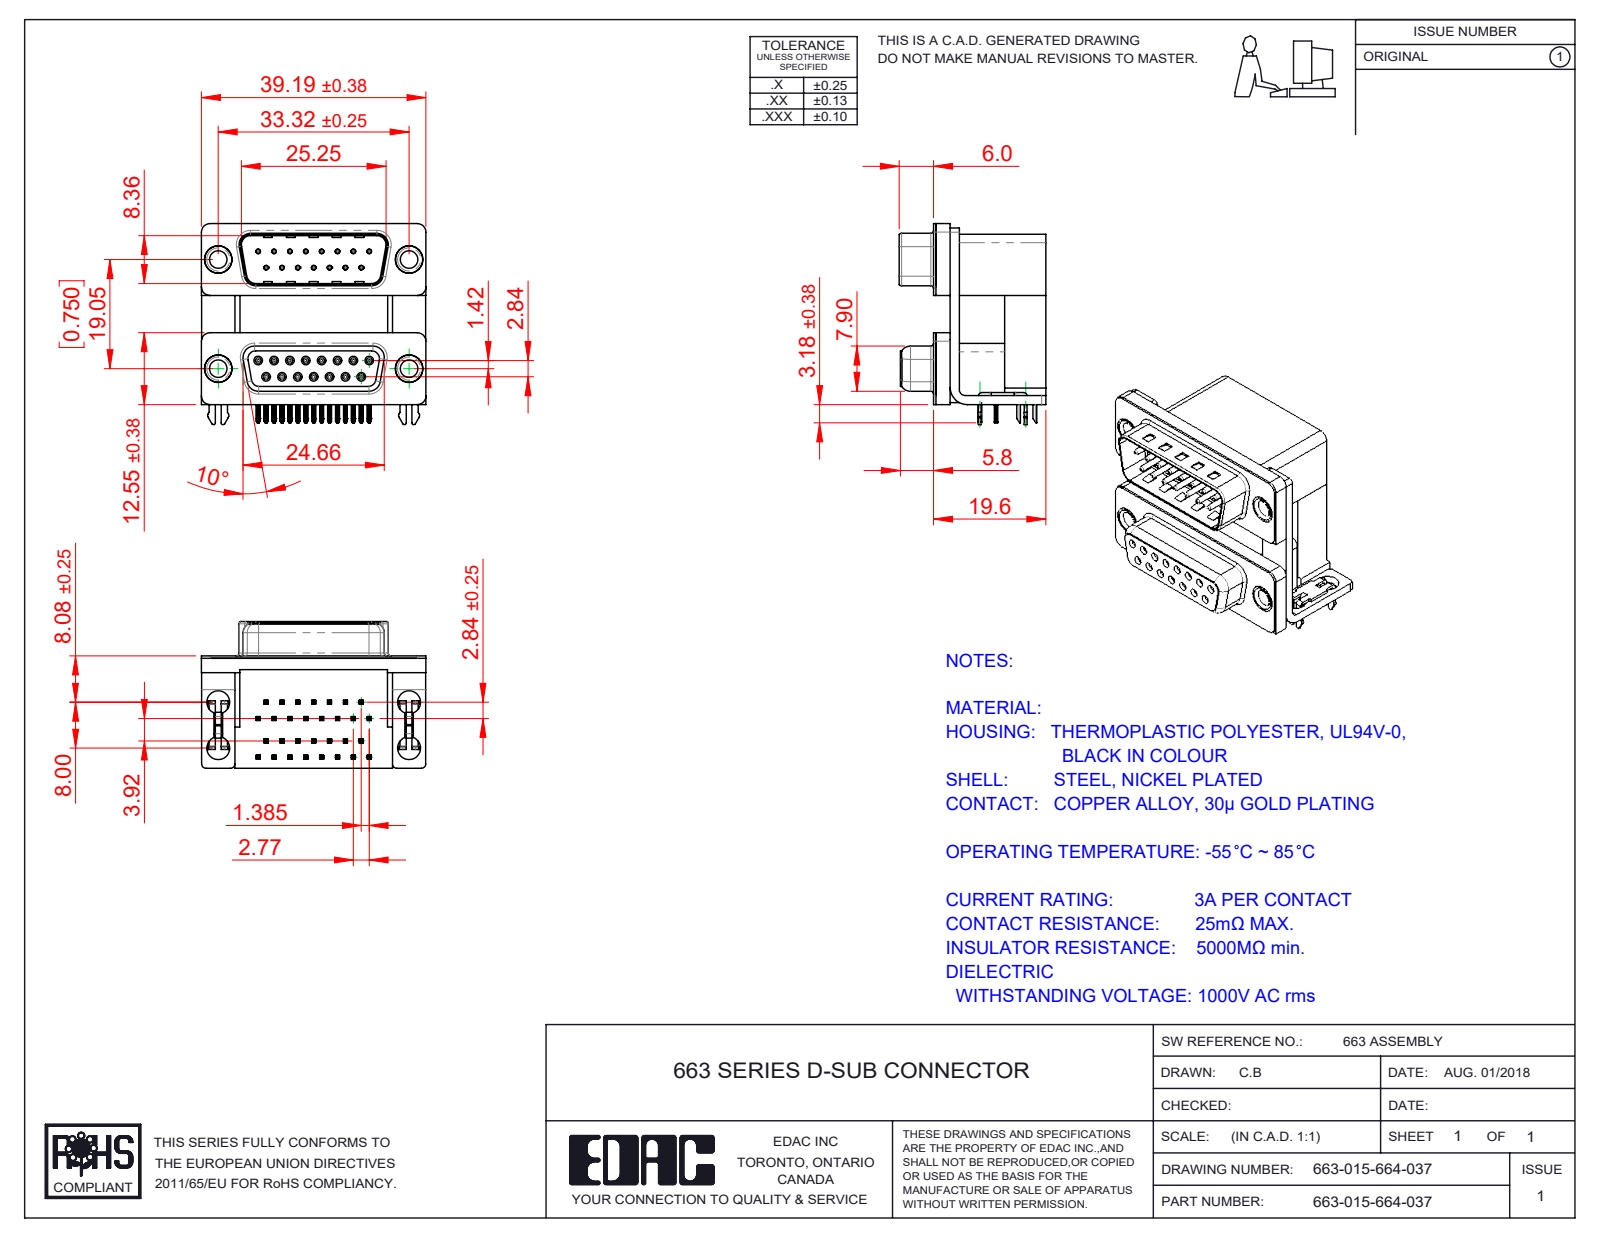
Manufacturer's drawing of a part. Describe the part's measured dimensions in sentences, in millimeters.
The part is named "663 2 Prong Board Lock_3; 663 Shell Receptacle_15 Contacts; 663 Thru Hole Rivet; 663-015-664-037 (+8 more)". Its 3-D file was written by "SolidWorks 2020 (CONFIG_CONTROL_DESIGN)". It is 43 solids with 3980 faces: 2117 planar, 1028 cylindrical and 835 other. Overall it measures 39.19 by 35.1 by 25.6 millimeters. Its volume is 15 212 cubic millimeters and its surface area 16 945 square millimeters. Round holes: 30 of diameter 0.8, 15 of diameter 0.35, 15 of diameter 0.9, 8 of diameter 4, 4 of diameter 3.05, 4 of diameter 3.5, 4 of diameter 4.8, 4 of diameter 5. Round bosses or shafts: 15 of diameter 1.2, 15 of diameter 0.75, 4 of diameter 4.9, 4 of diameter 4.75, 4 of diameter 3.85. Partial cylindrical surfaces (rounded edges, fillets, slot ends): 122 of radius 0.1, 70 of radius 0.25, 60 of radius 0.15, 30 of radius 0.12, 30 of radius 0.35, 16 of radius 0.5, 16 of radius 1.5, 15 of radius 0.34. The main face-to-face distances are 0.4, 19.2, 16.7, 2.5, 7.2, 12, 9.5, 10.69, 1.6, 2.9. The hole center spacings are 3.16, 19.25, 2.77, 19.84, 5.54, 8.31, 19.05, 20.78.
